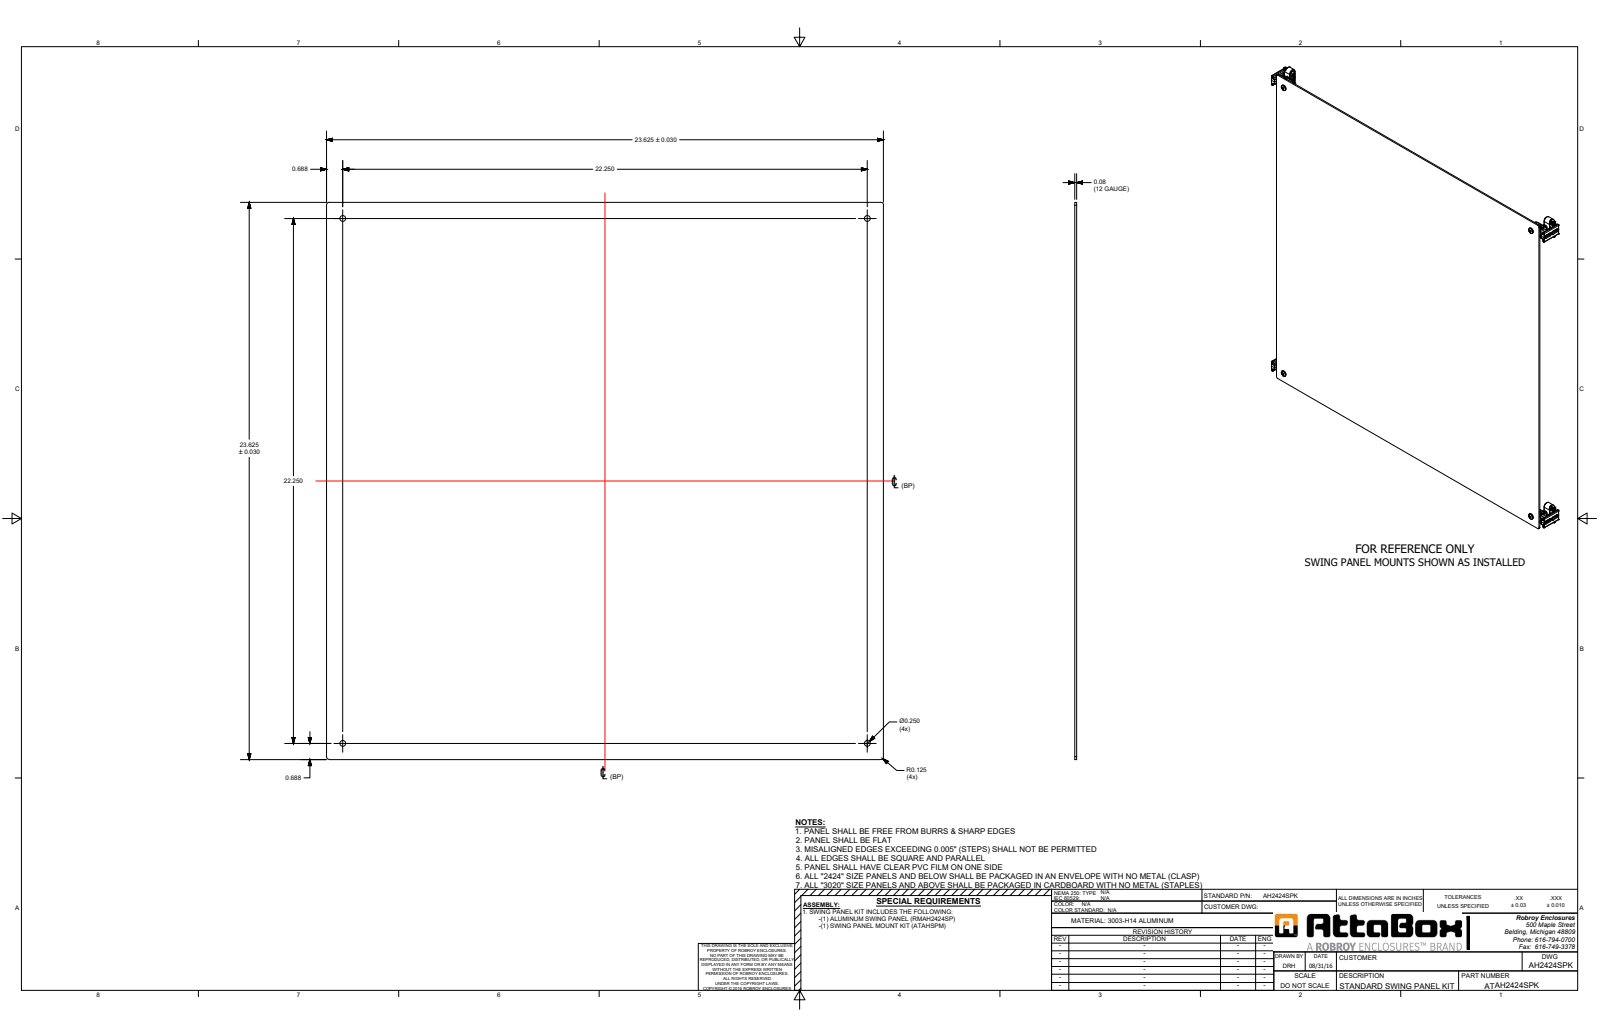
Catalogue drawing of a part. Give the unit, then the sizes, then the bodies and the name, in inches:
Units: inches
Overall size (bounding box): 24.559 × 23.625 × 1.448
Round holes (diameter × count): ⌀0.156 ×8, ⌀0.25 ×8
Round bosses / shafts (diameter × count): ⌀0.373 ×8, ⌀0.262 ×8, ⌀0.19 ×8
Partial cylindrical surfaces — rounded edges, fillets, slot ends (radius × count): R0.035 ×248, R0.02 ×124, R0.065 ×54, R0.015 ×30, R0.045 ×16, R0.05 ×16, R0.025 ×14, R0.9 ×8
Main face-to-face distances: 0.08, 22.25, 0.378, 0.378, 23.625, 23.625, 0.5, 0.51, 0.59, 24.559
Hole centre spacings: 22.25, 0.875, 22.25, 31.466, 21.375, 23.125
Volume: 47.72 in³ · Surface area: 1 181 in²
Bodies: 33 solids, 2010 faces (518 planar, 736 cylindrical, 756 other)
Part name (STEP PRODUCT): AH2424SPK
STEP written by: SolidWorks 2019 (AUTOMOTIVE_DESIGN)
